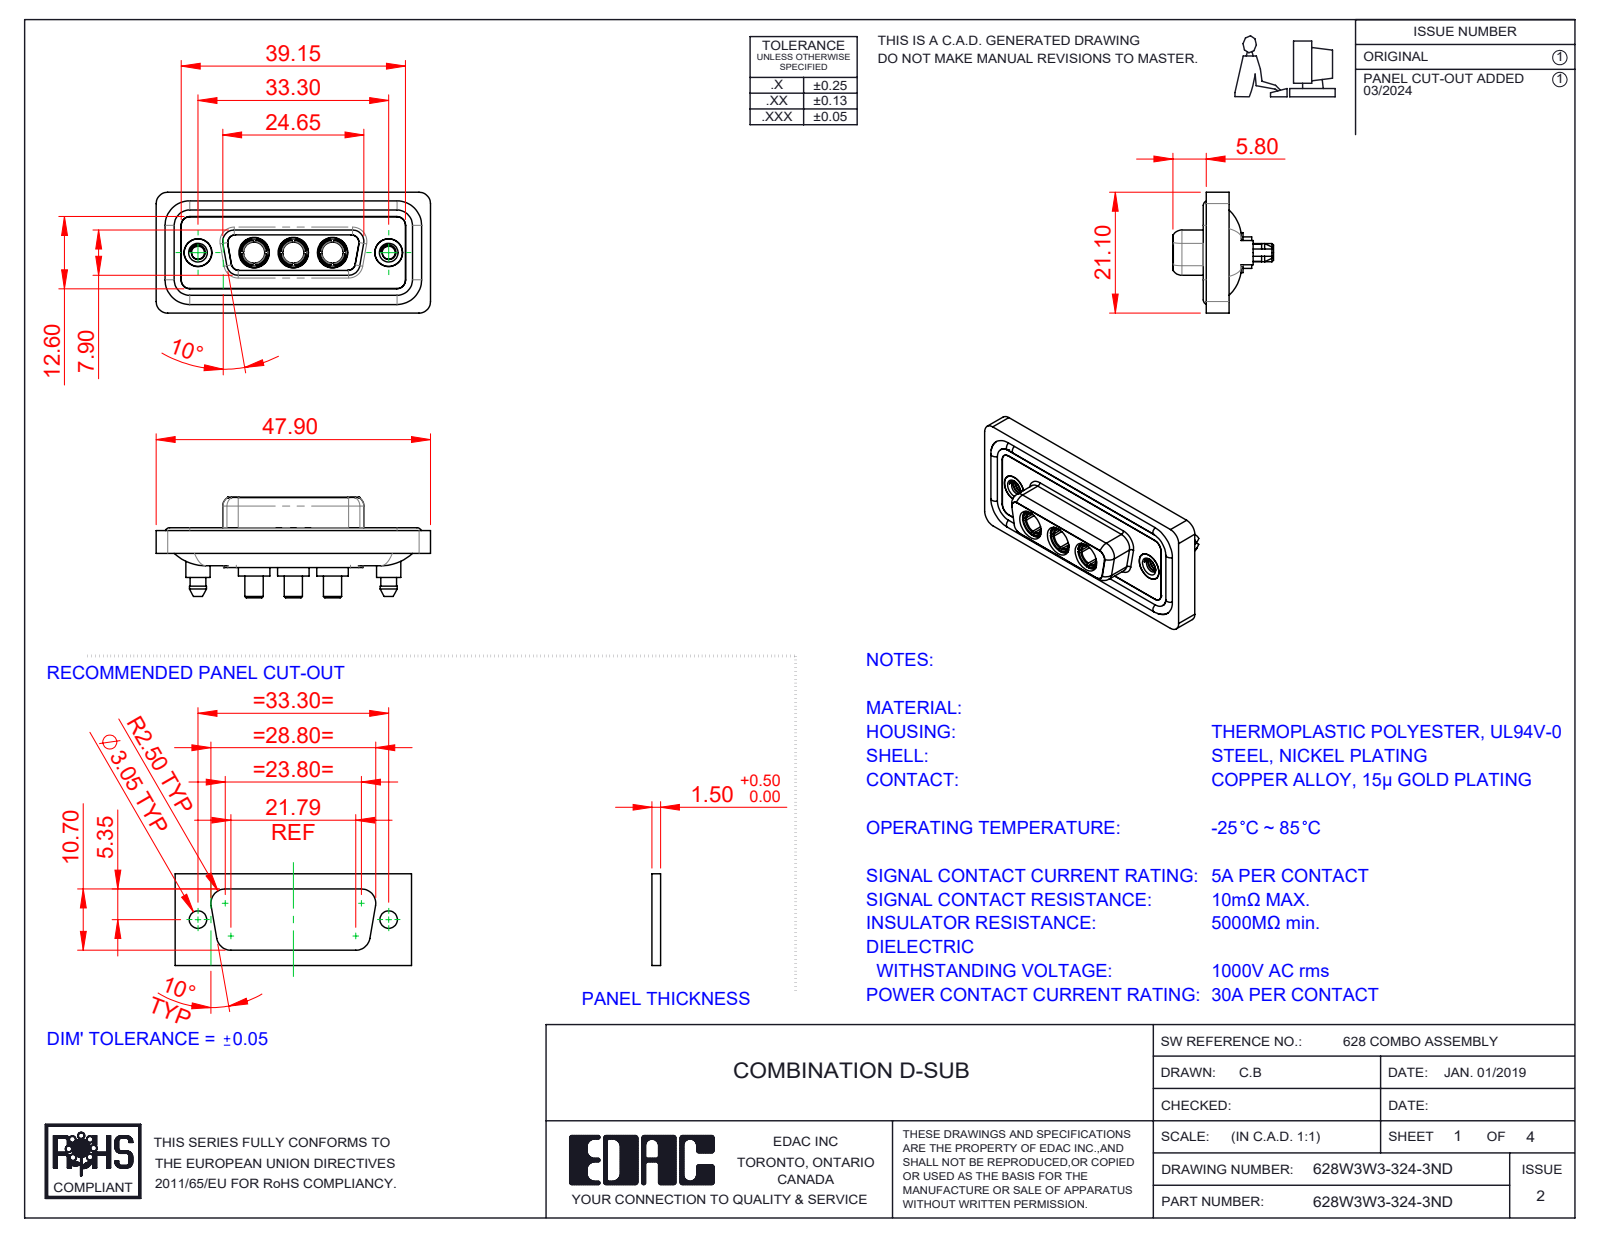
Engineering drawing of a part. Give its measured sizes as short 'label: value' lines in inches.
name: 628Combo Shell Front_15 Contacts; Power Socket_30A S; 628Combo Threaded Boardlock_D; 628Combo Shell Rear_15 Contacts (+3 more)
written by: SolidWorks 2023 (CONFIG_CONTROL_DESIGN)
unit: in
bodies: 13 solids, 674 faces (208 planar, 305 cylindrical, 161 other)
size: 1.886 × 0.831 × 0.691
volume: 0.377 in³; area: 15.64 in²
holes: 5× ⌀0.191, 3× ⌀0.146, 3× ⌀0.209, 2× ⌀0.089, 2× ⌀0.157, 2× ⌀0.159, 2× ⌀0.197
bosses: 4× ⌀0.063, 3× ⌀0.217, 3× ⌀0.205, 3× ⌀0.195, 3× ⌀0.187, 3× ⌀0.148, 3× ⌀0.126, 2× ⌀0.213
rounds: 24× R0.059, 20× R0.079, 12× R0.053, 10× R0.063, 4× R0.01, 4× R0.02, 4× R0.024, 4× R0.026
face distances: 0.016, 0.071, 0.063, 0.02, 0.293, 0.043, 0.114, 0.222, 0.278, 0.26
hole spacings: 0.27, 0.386, 0.656, 0.925, 0.539, 1.311
